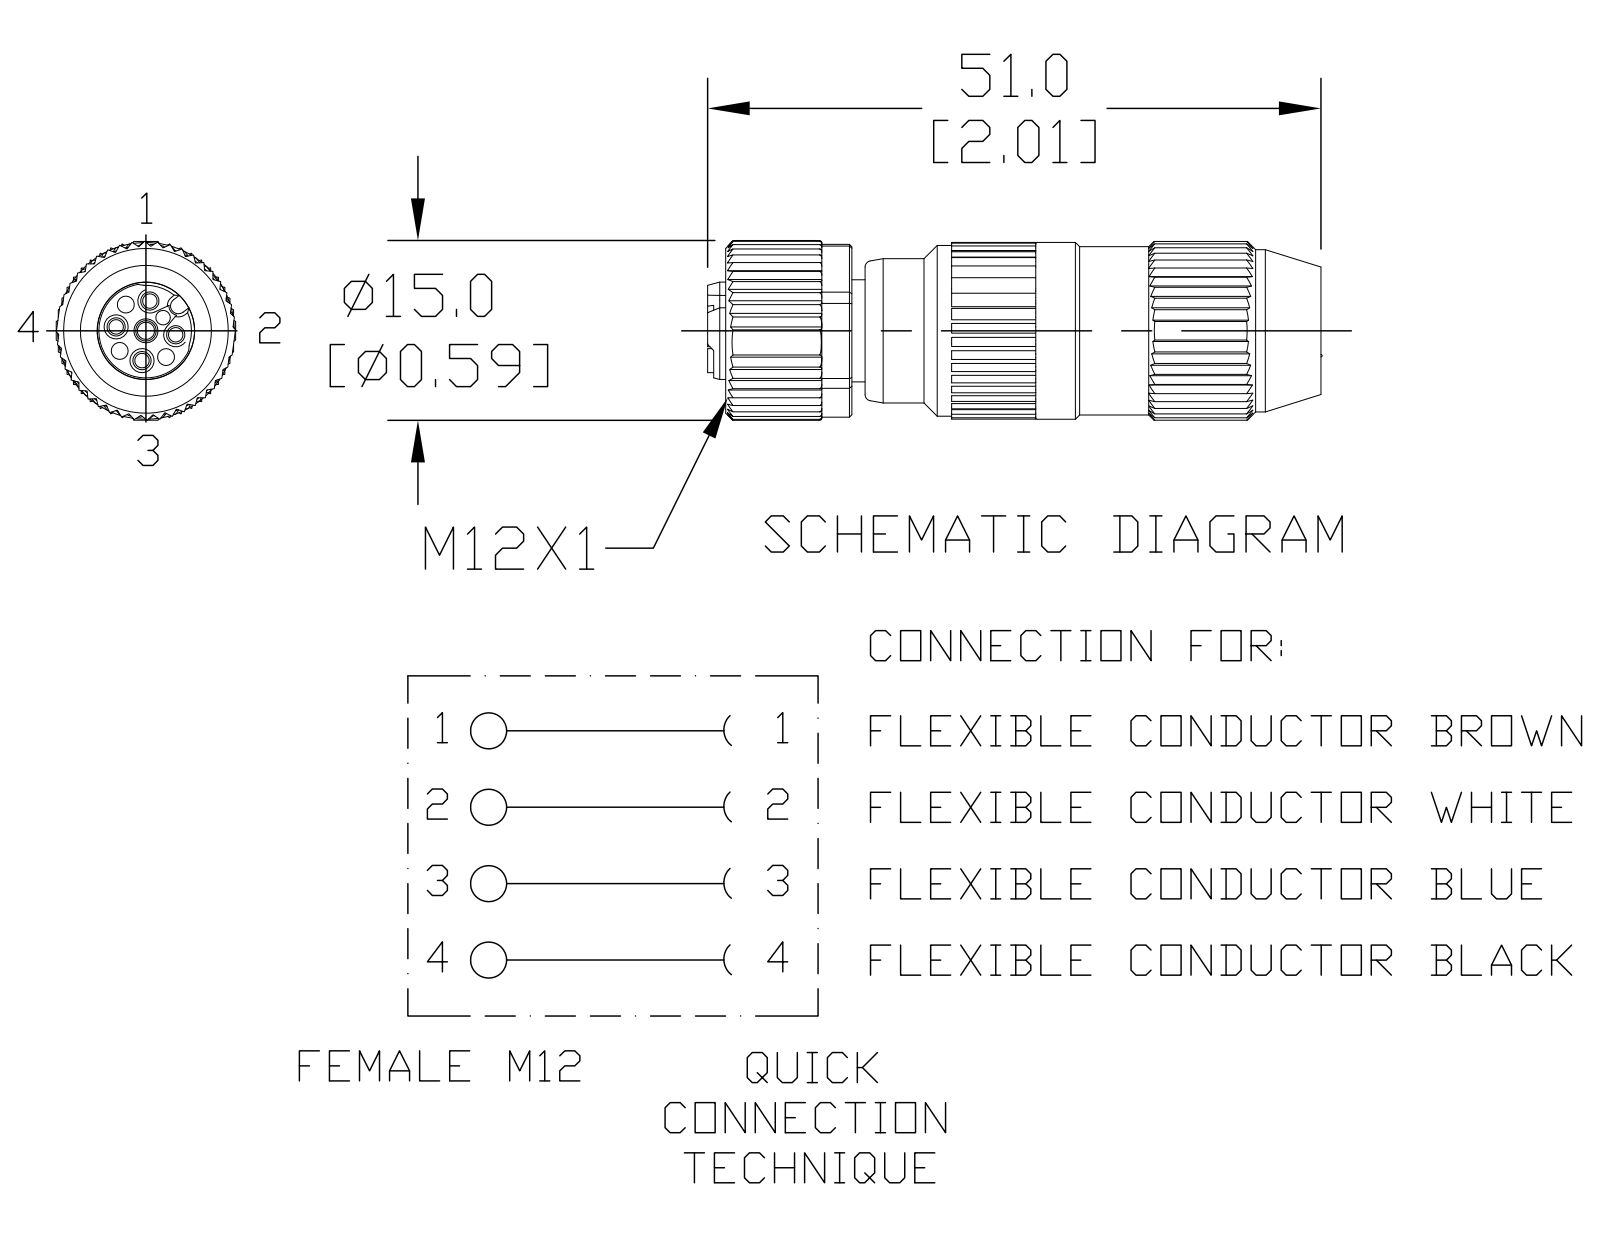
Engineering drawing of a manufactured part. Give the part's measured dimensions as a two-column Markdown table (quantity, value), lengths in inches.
| quantity | value |
| --- | --- |
| part name | 7000-12601-0000000 |
| STEP written by | SolidWorks 2015 (AUTOMOTIVE_DESIGN) |
| units | inches |
| bodies | 1 solid, 566 faces (320 planar, 179 cylindrical, 67 other) |
| overall size | 51 × 15 × 15 |
| volume | 6 737 in³ |
| surface area | 4 106 in² |
| round holes (diameter × count) | 1 × 5, 6.1 × 1, 11 × 1 |
| round bosses / shafts (diameter × count) | 15 × 1, 13.827 × 1, 13.6 × 1, 12 × 1, 9.047 × 1, 8.12 × 1 |
| partial cylindrical surfaces (radius × count) | 0.5 × 1, 7.496 × 1 |
| main face-to-face distances | 16.534, 8, 2, 40.46, 9.46, 39, 48.46, 2.54, 51, 12 |
| hole center spacings | 2.5, 3.535, 5 |
